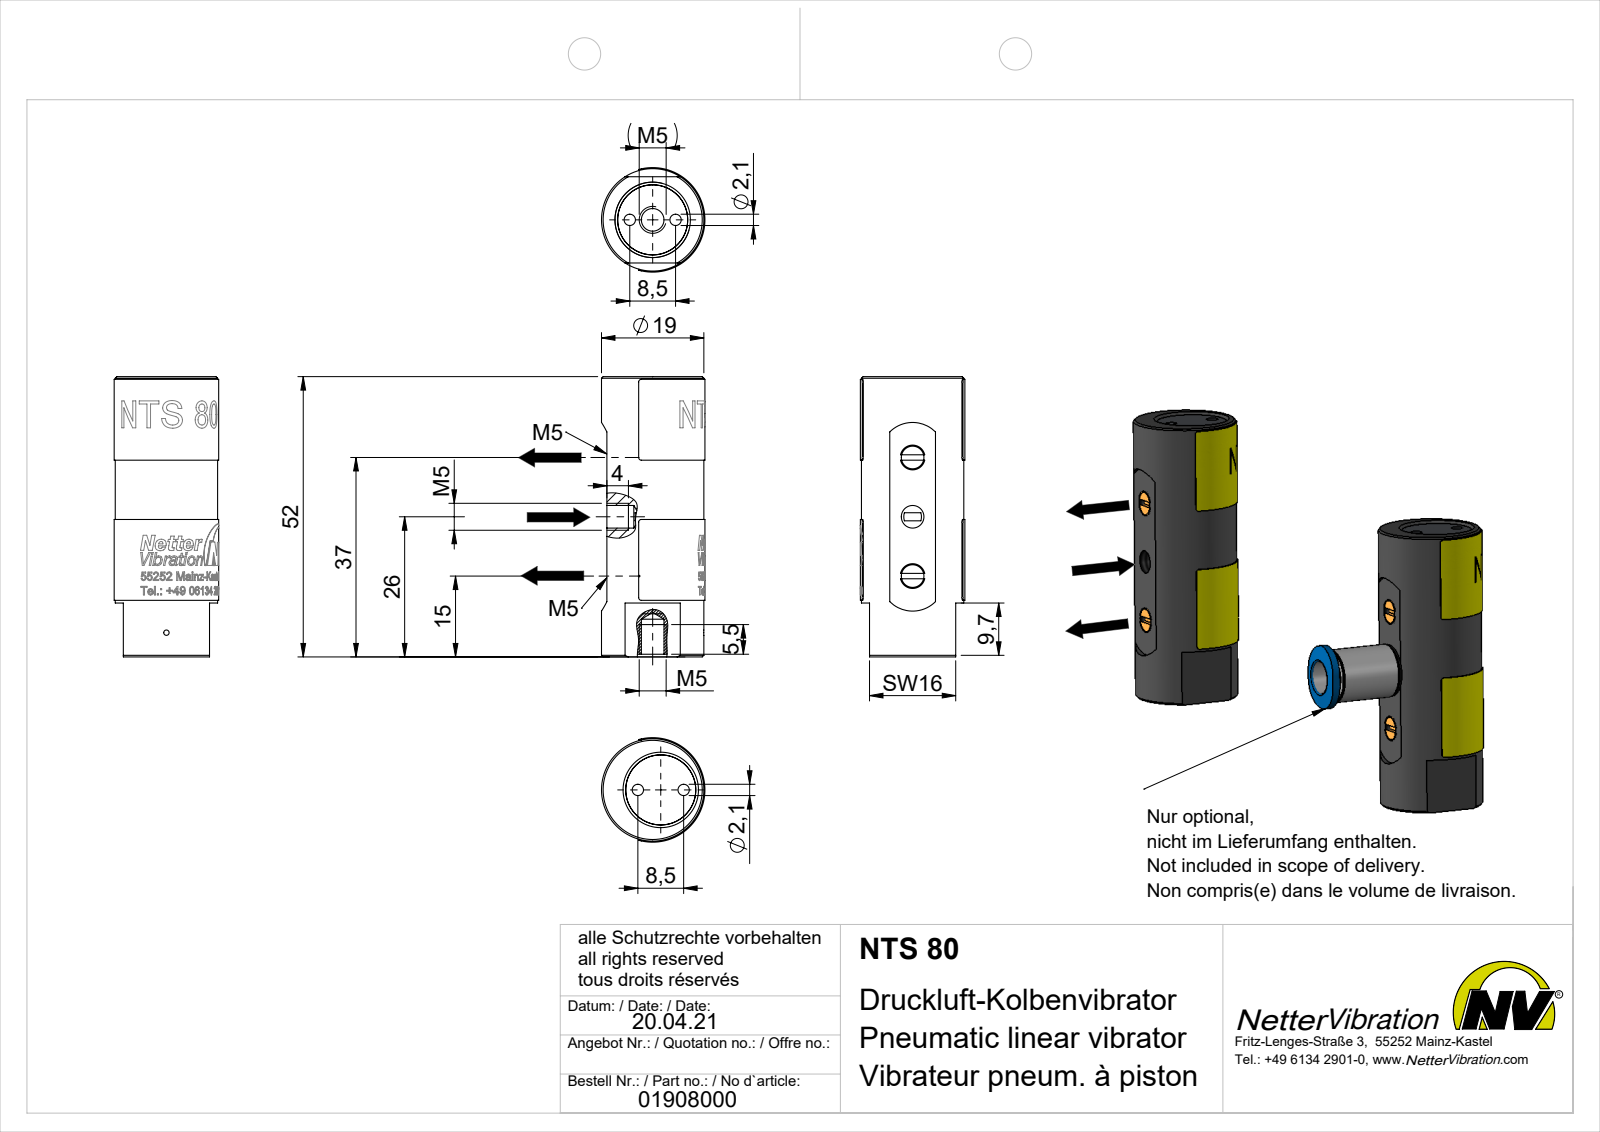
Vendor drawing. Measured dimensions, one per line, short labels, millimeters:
name: NTS 80 Kolbenvibrator #01908000
written by: SolidWorks 2015 (AUTOMOTIVE_DESIGN)
unit: mm
bodies: 7 solids, 225 faces (84 planar, 58 cylindrical, 83 other)
size: 52 × 19.4 × 19.2
volume: 14 658 mm³; area: 8 467 mm²
holes: 4× ⌀2.3, 4× ⌀4.2, 3× ⌀1, 2× ⌀13, 1× ⌀7.2, 1× ⌀9, 1× ⌀19
bosses: 2× ⌀14, 2× ⌀5
rounds: 8× R0.5, 2× R6, 1× R9.7
face distances: 7.5, 43.5, 0.5, 8, 44, 51.5, 36, 8.75, 43.25, 8.25
hole spacings: 4.25, 1.5, 2.75, 5.75, 8.5, 11, 7, 10
